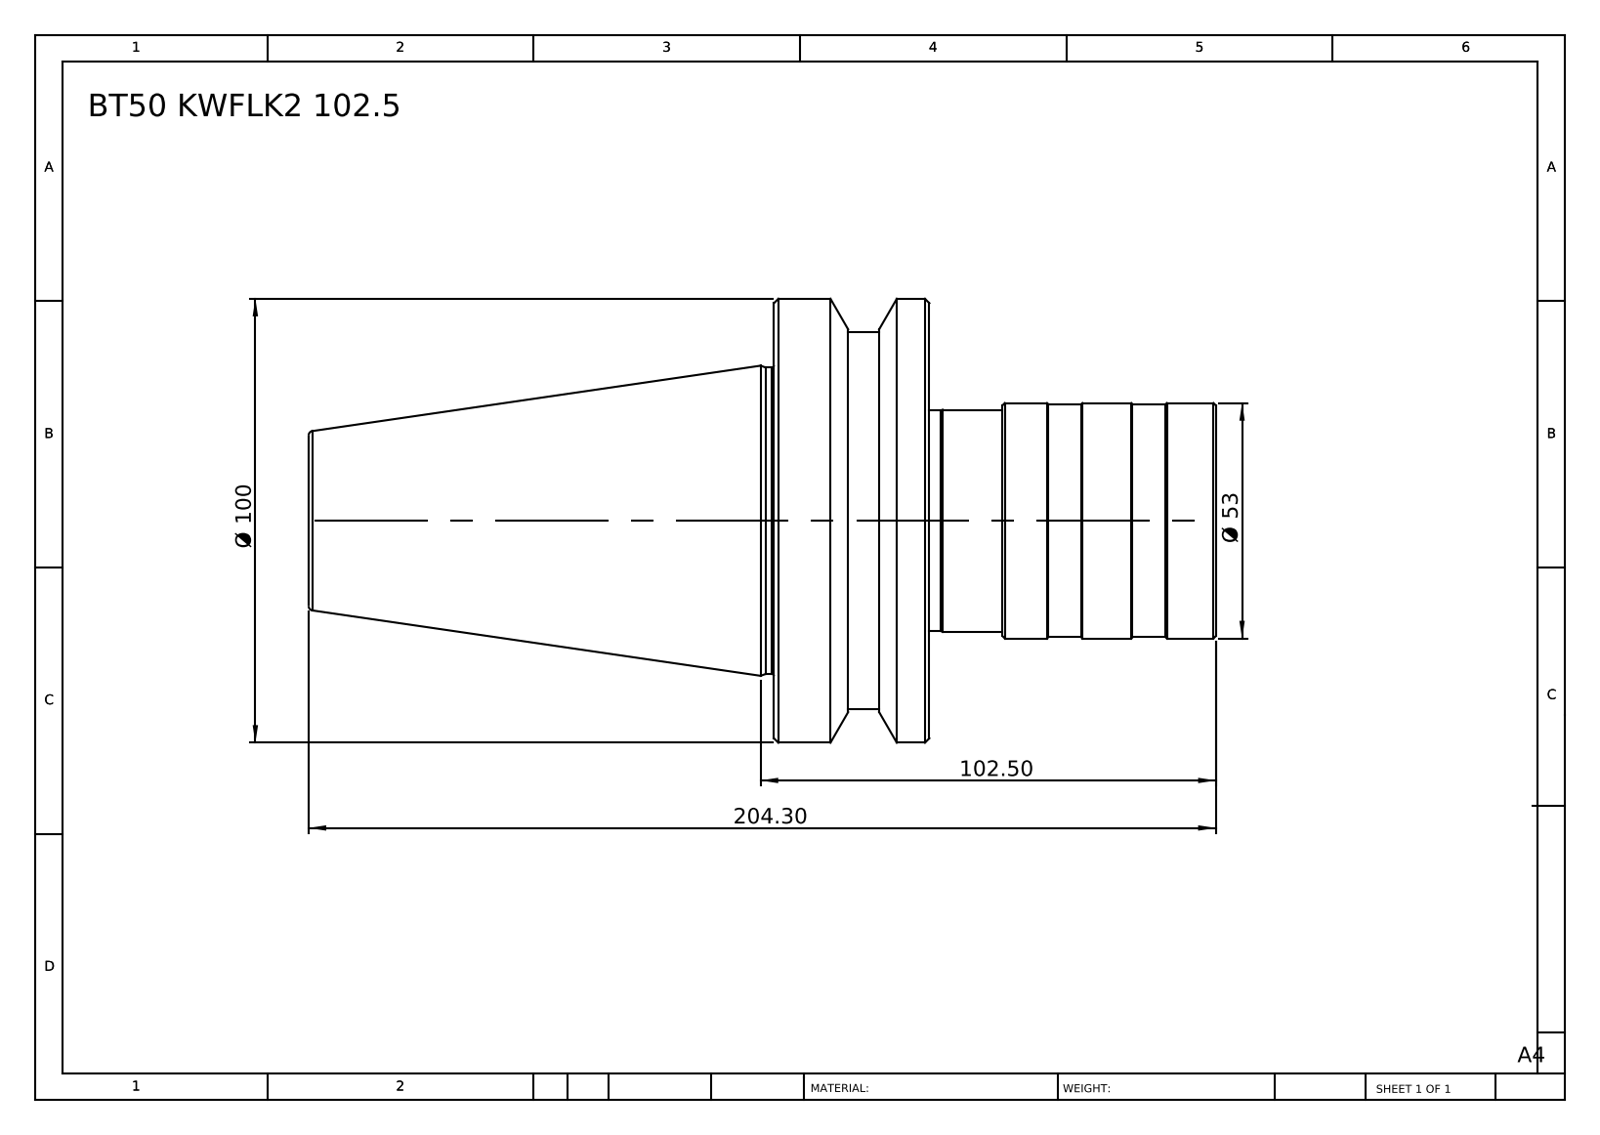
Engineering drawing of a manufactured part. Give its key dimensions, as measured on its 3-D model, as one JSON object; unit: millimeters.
{"part_name": "BT50 KWFLK2 102.5", "step_written_by": "SolidWorks 2014 (CONFIG_CONTROL_DESIGN)", "units": "millimeters", "bodies": {"solids": 1, "faces": 59, "planar": 7, "cylindrical": 22, "other": 30}, "overall_size": [204.3, 100, 100], "volume_mm3": 647683, "surface_area_mm2": 55426, "round_bosses_or_shafts": [[100, 1], [85, 1], [69, 1], [53, 1], [52.5, 1], [50, 1], [49.6, 1]], "face_to_face_distances": [35, 64.5, 99.5, 204.3, 139.8, 104.8, 82.8, 18.3, 16.7, 121.5]}
